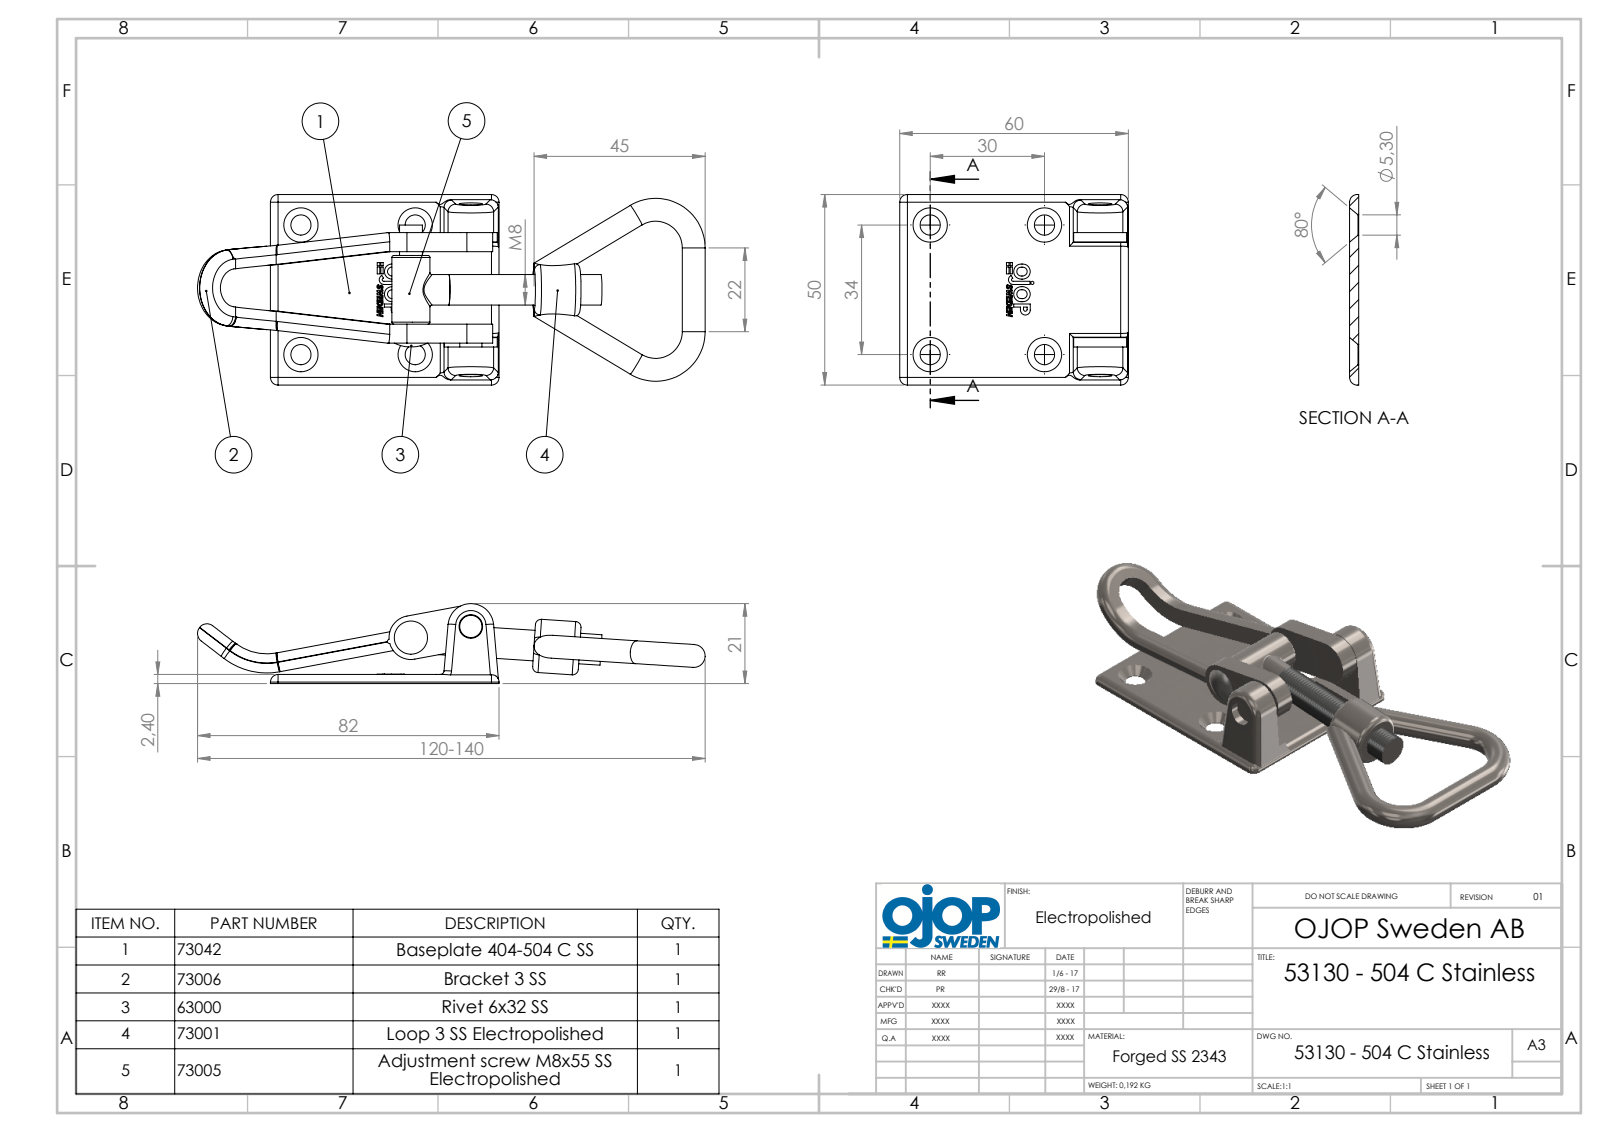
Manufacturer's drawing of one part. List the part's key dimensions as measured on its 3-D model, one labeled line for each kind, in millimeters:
Part name (STEP PRODUCT): 404-504 C RF; bygel 3; Hålnit 6x32; Ring 3 (+2 more)
STEP written by: SolidWorks 2015 (AUTOMOTIVE_DESIGN)
Units: millimetres
Bodies: 5 solids, 204 faces (56 planar, 83 cylindrical, 65 other)
Overall size (bounding box): 134.53 × 50 × 21.15
Volume: 24 109 mm³ · Surface area: 17 917 mm²
Round holes (diameter × count): ⌀5.3 ×4, ⌀6.2 ×2, ⌀3 ×1, ⌀6.3 ×1, ⌀8.1 ×1
Round bosses / shafts (diameter × count): ⌀6 ×4, ⌀10 ×1, ⌀8.01 ×1, ⌀8 ×1, ⌀5.85 ×1
Partial cylindrical surfaces — rounded edges, fillets, slot ends (radius × count): R2 ×8, R2.5 ×8, R1 ×4, R6.99 ×4, R1.5 ×2, R6.15 ×2, R2.4 ×1, R5 ×1
Main face-to-face distances: 2.4, 5, 25, 30, 20, 3.68, 8.68, 1, 6, 12.3
Hole centre spacings: 30, 34, 45.34, 16.01
